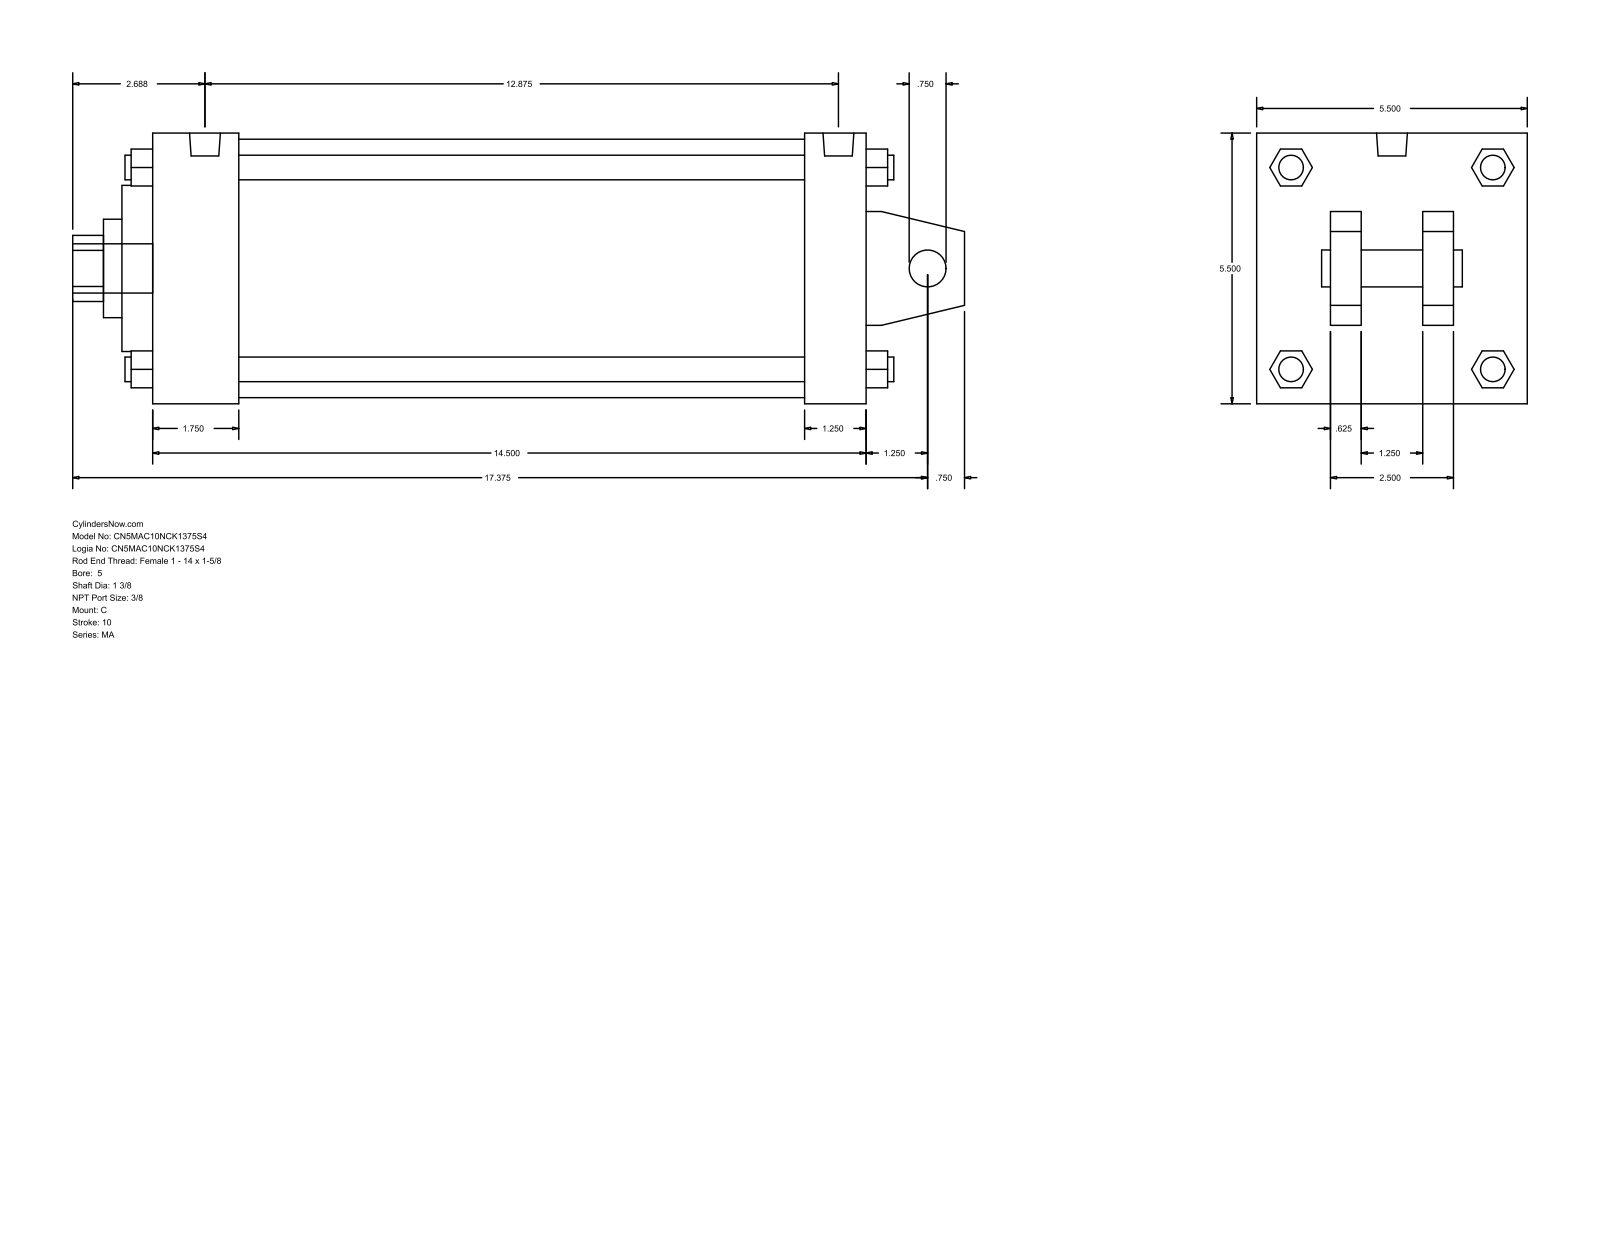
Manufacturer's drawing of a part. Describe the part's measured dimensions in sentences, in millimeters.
The part is named "MA_C__0500_1.375". Its 3-D file was written by "GSSL Pune (CONFIG_CONTROL_DESIGN)". It is 0 solids with 141 faces: 109 planar, 32 cylindrical and 0 other. Overall it measures 460.38 by 139.7 by 139.7 millimeters. Round holes: 1 of diameter 19.05, 1 of diameter 34.92, 1 of diameter 50.8, 1 of diameter 85.72, 1 of diameter 133.35. Round bosses or shafts: 4 of diameter 12.7, 4 of diameter 11.11, 2 of diameter 15.93, 1 of diameter 25.4. Partial cylindrical surfaces (rounded edges, fillets, slot ends): 1 of radius 17.06. The main face-to-face distances are 139.7, 368.3, 15.87, 336.55, 31.75, 44.45, 292.1, 323.85, 38.1, 101.6.
